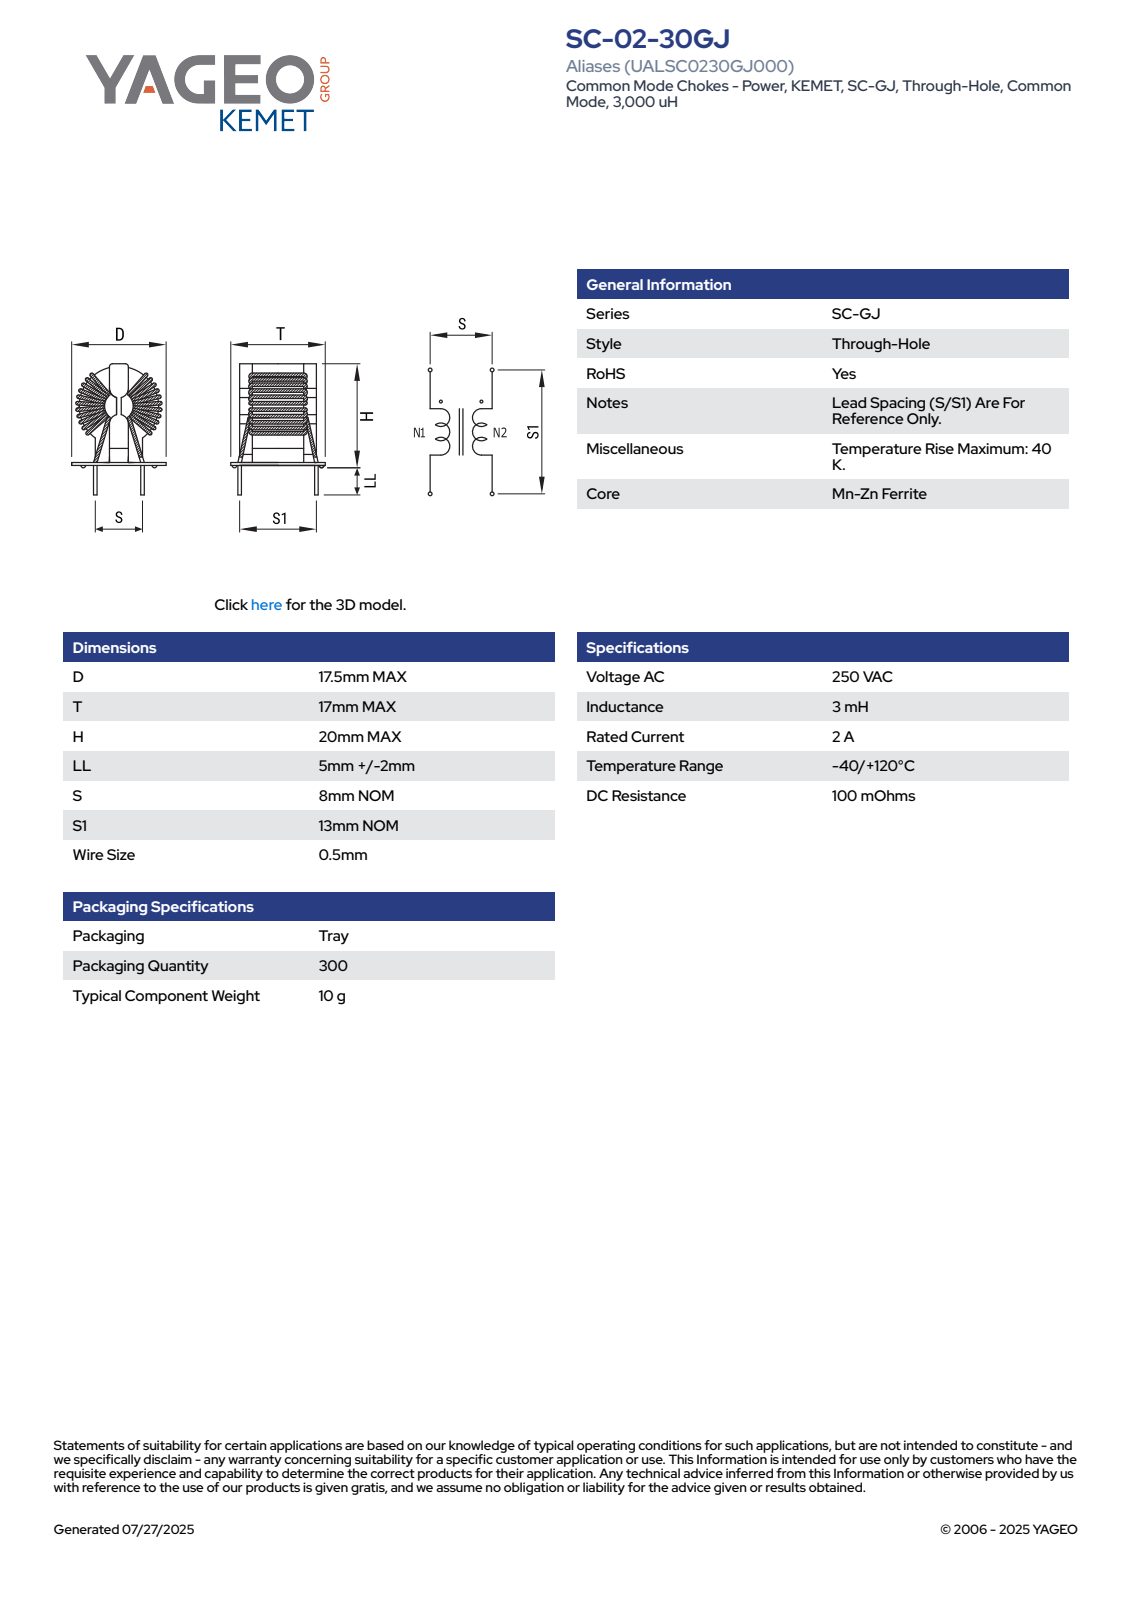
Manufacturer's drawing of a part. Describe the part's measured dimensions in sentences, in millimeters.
The part is named "SC-02-30GJ". Its 3-D file was written by "SolidWorks 2018 (AUTOMOTIVE_DESIGN)". It is 4 solids with 395 faces: 167 planar, 128 cylindrical and 100 other. Overall it measures 25 by 17.5 by 17 millimeters. Its volume is 3 535 cubic millimeters and its surface area 3 583 square millimeters. Round holes: 1 of diameter 7.3, 1 of diameter 12.8. Round bosses or shafts: 8 of diameter 0.5, 1 of diameter 13.9, 1 of diameter 7.25. Partial cylindrical surfaces (rounded edges, fillets, slot ends): 20 of radius 0.5, 16 of radius 0.25, 6 of radius 0.2, 4 of radius 1, 4 of radius 1.6, 3 of radius 0.3, 2 of radius 0.9, 2 of radius 2. The main face-to-face distances are 1.4, 2, 9.97, 3.2, 1.03, 1.2, 11, 3.03, 7.97, 9.98.
